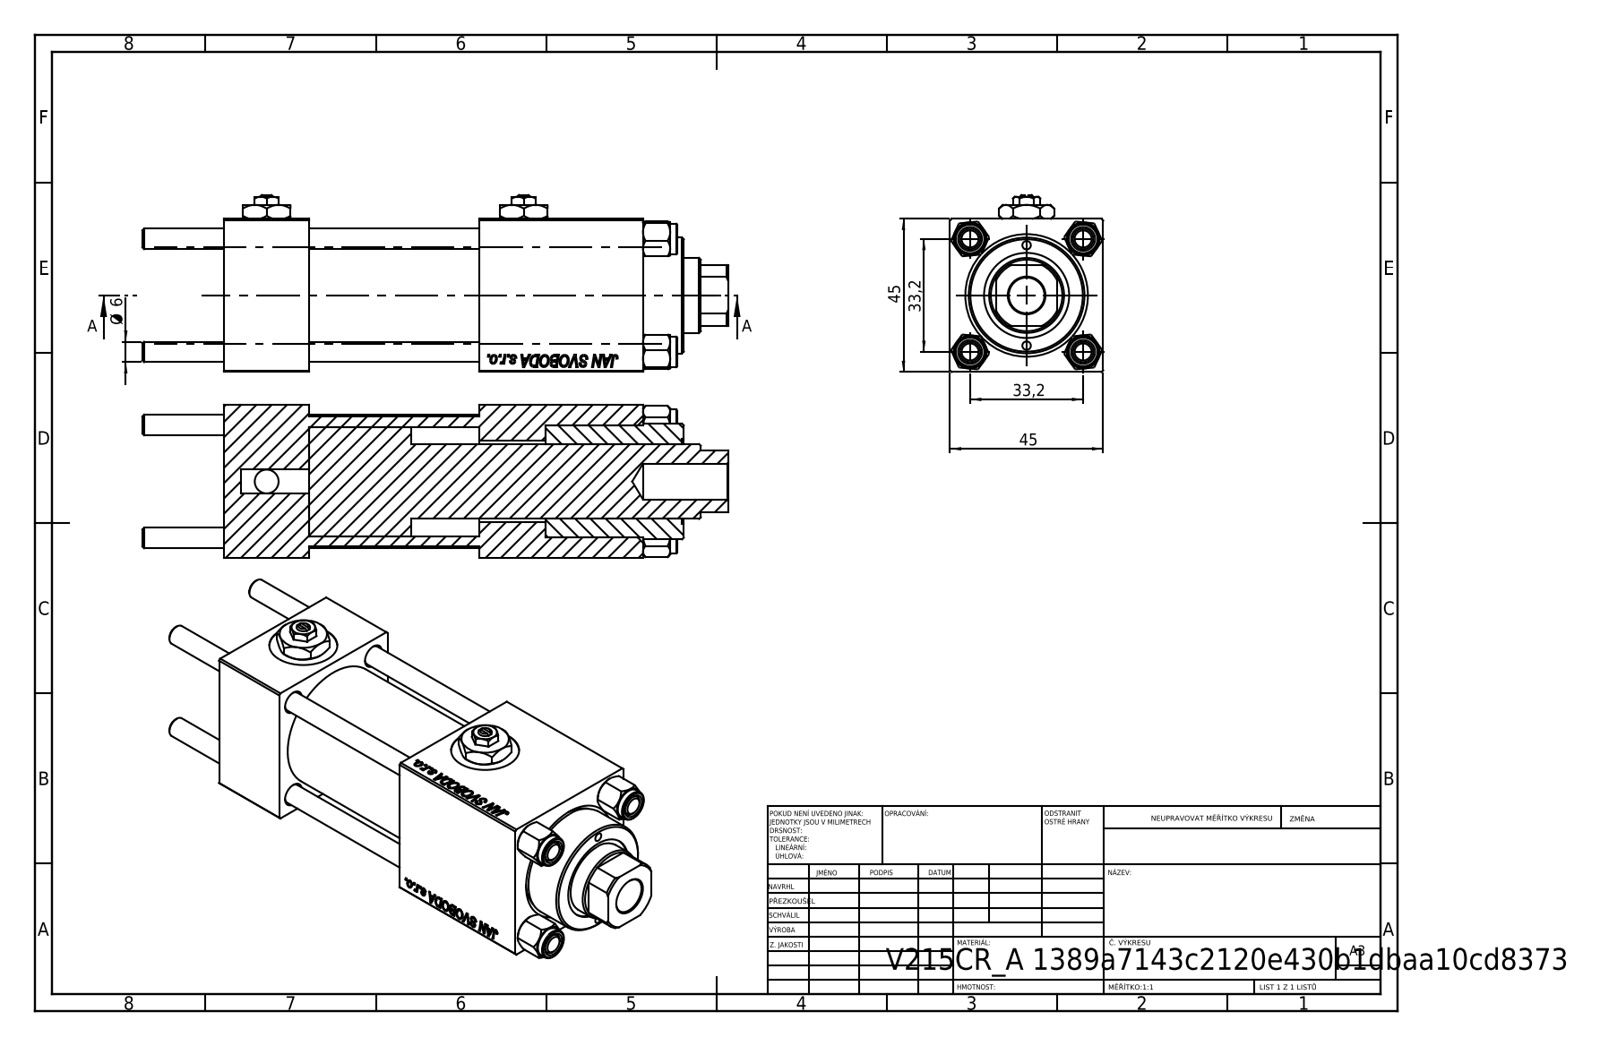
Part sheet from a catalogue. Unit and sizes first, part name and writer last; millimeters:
Units: millimetres
Overall size (bounding box): 172 × 52 × 45
Round holes (diameter × count): ⌀6 ×4, ⌀2.5 ×2, ⌀7 ×2, ⌀13.16 ×2, ⌀20 ×2, ⌀10.5 ×1, ⌀22 ×1, ⌀24 ×1, ⌀25 ×1, ⌀32 ×1, ⌀33 ×1
Round bosses / shafts (diameter × count): ⌀9 ×4, ⌀38 ×1, ⌀34 ×1
Partial cylindrical surfaces — rounded edges, fillets, slot ends (radius × count): R10.5 ×1
Main face-to-face distances: 45, 25, 123, 50, 75, 98, 48, 44.8, 94.3, 69.3
Hole centre spacings: 16.7, 23.48, 33.2, 35.47, 14.75, 46.95, 29.5, 75.5
Volume: 212 553 mm³ · Surface area: 79 149 mm²
Bodies: 13 solids, 1238 faces (568 planar, 92 cylindrical, 578 other)
Part name (STEP PRODUCT): Zatka_pro_OIL_PORT; V215_VC_A; V215CR_VCP; V215CR_BODY_A (+2 more)
STEP written by: SolidWorks 2019 (CONFIG_CONTROL_DESIGN)
